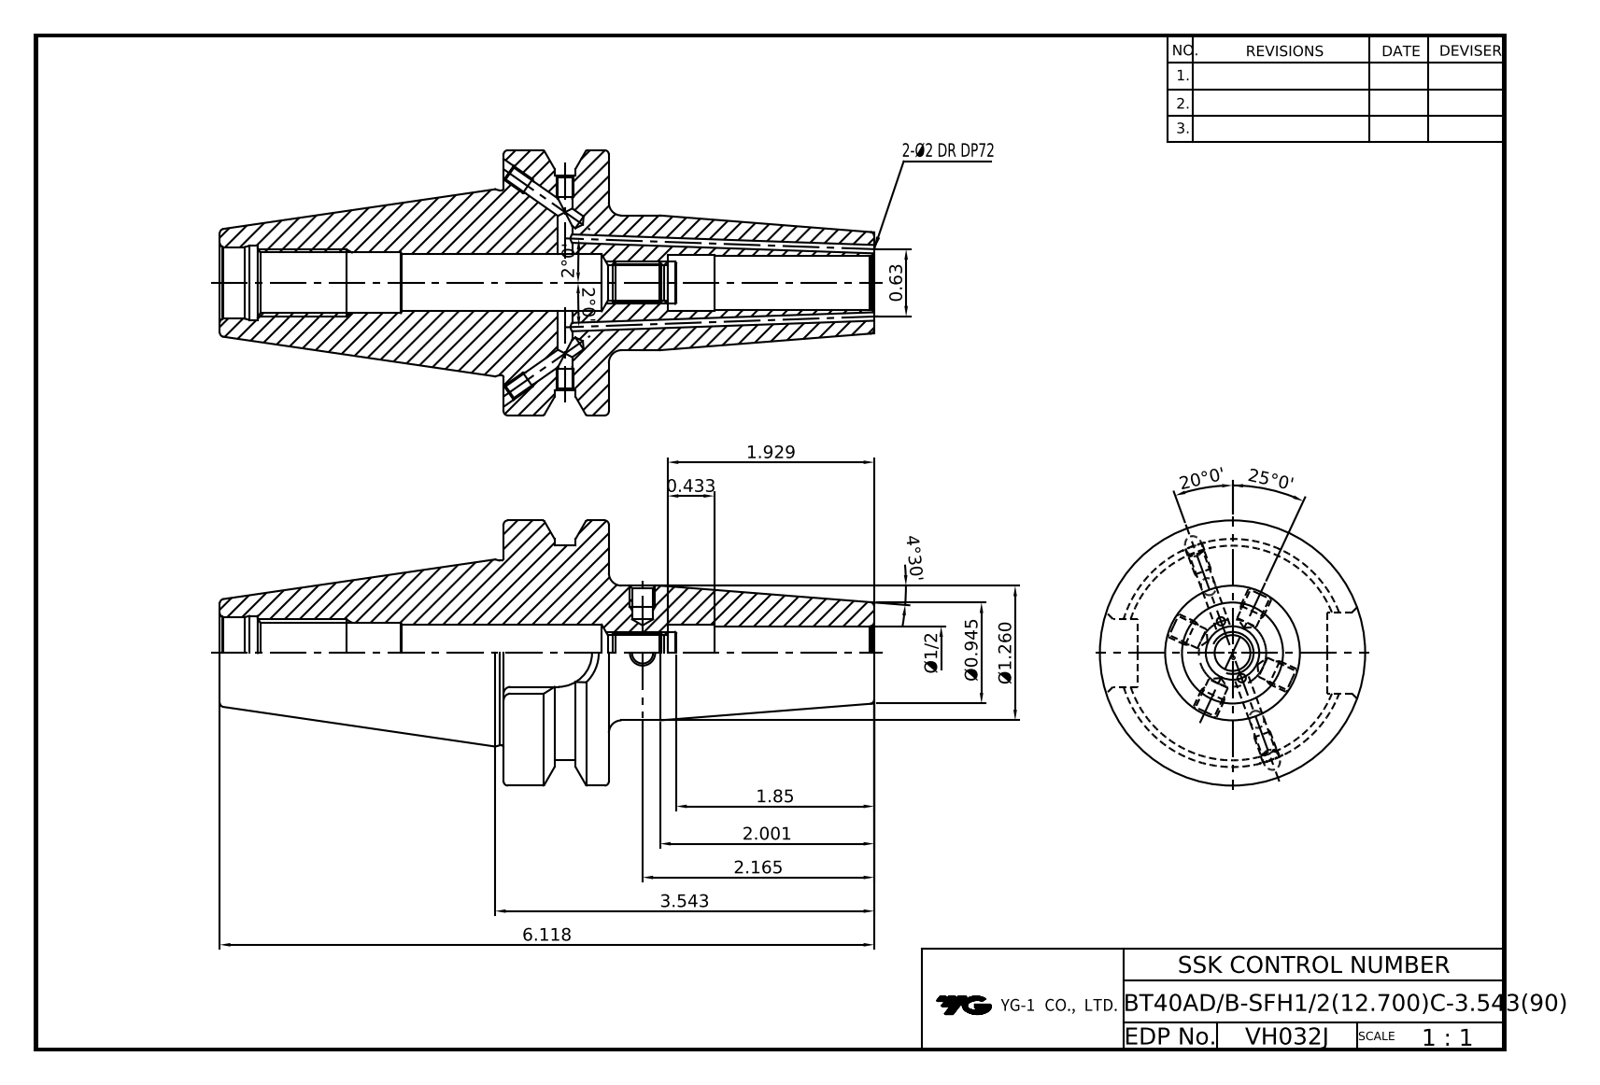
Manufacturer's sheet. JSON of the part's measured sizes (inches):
{"part_name": "LO-BT40ADB-SFH12.7C-90", "step_written_by": "Autodesk Inventor 2022 (AUTOMOTIVE_DESIGN)", "units": "inches", "bodies": {"solids": 1, "faces": 76, "planar": 23, "cylindrical": 30, "other": 23}, "overall_size": [6.118, 2.48, 2.48], "volume_in3": 9.311, "surface_area_in2": 49.16, "round_holes": [[0.128, 4], [0.157, 4], [0.098, 2], [0.351, 1], [0.5, 1], [0.531, 1], [0.545, 1], [0.547, 1], [0.669, 1], [0.693, 1]], "round_bosses_or_shafts": [[2.48, 1], [2.008, 1], [1.732, 1], [1.26, 1]], "partial_cylinders_radius": [[0.317, 1]], "face_to_face_distances": [0.984, 1.78, 0.673, 0.311, 0.476, 0.197, 0.508, 3.465, 2.988, 2.791]}
